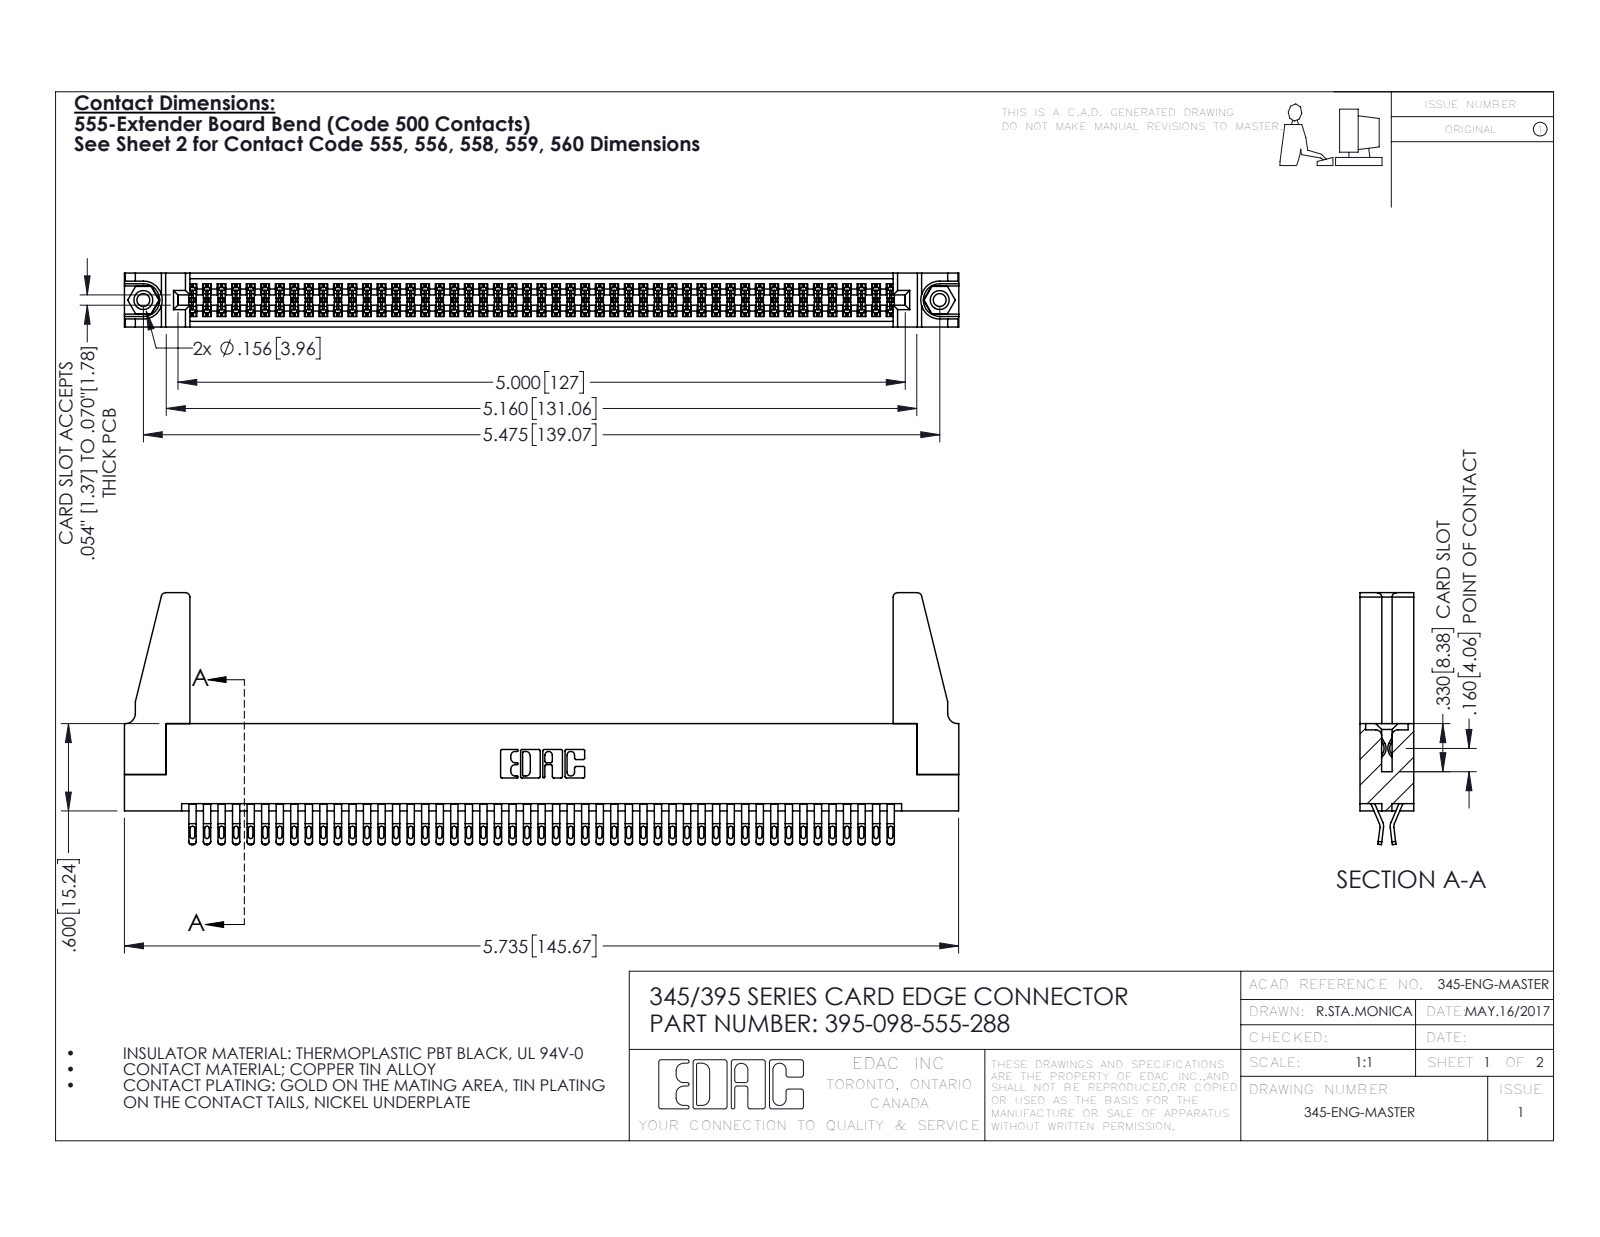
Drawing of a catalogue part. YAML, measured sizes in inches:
part_name: "345 Part_Flush Mounting Lugs - 0.156 Dia-TH; 345-250-001_345-250-001-102; 345-292-001_555 Tail; 395-098-555-288 (+1 more)"
step_written_by: "SolidWorks 2016 (CONFIG_CONTROL_DESIGN)"
units: inches
bodies: {solids: 103, faces: 5738, planar: 3190, cylindrical: 2532, other: 16}
overall_size: [5.736, 1.732, 0.37]
volume: 1.083
surface_area: 39.81
round_holes:
  - {diameter: 0.089, count: 2}
  - {diameter: 0.125, count: 2}
  - {diameter: 0.156, count: 2}
  - {diameter: 0.064, count: 1}
round_bosses_or_shafts:
  - {diameter: 0.155, count: 2}
partial_cylinders:
  - {radius: 0.016, count: 245}
  - {radius: 0.02, count: 196}
  - {radius: 0.006, count: 147}
  - {radius: 0.01, count: 22}
  - {radius: 0.03, count: 8}
  - {radius: 0.007, count: 6}
  - {radius: 0.031, count: 6}
  - {radius: 0.026, count: 3}
face_to_face_distances: [0.072, 0.298, 0.37, 0.025, 0.2, 0.098, 0.272, 0.225, 0.175, 0.149]
hole_center_spacings: [0.27, 5.239, 5.475]
